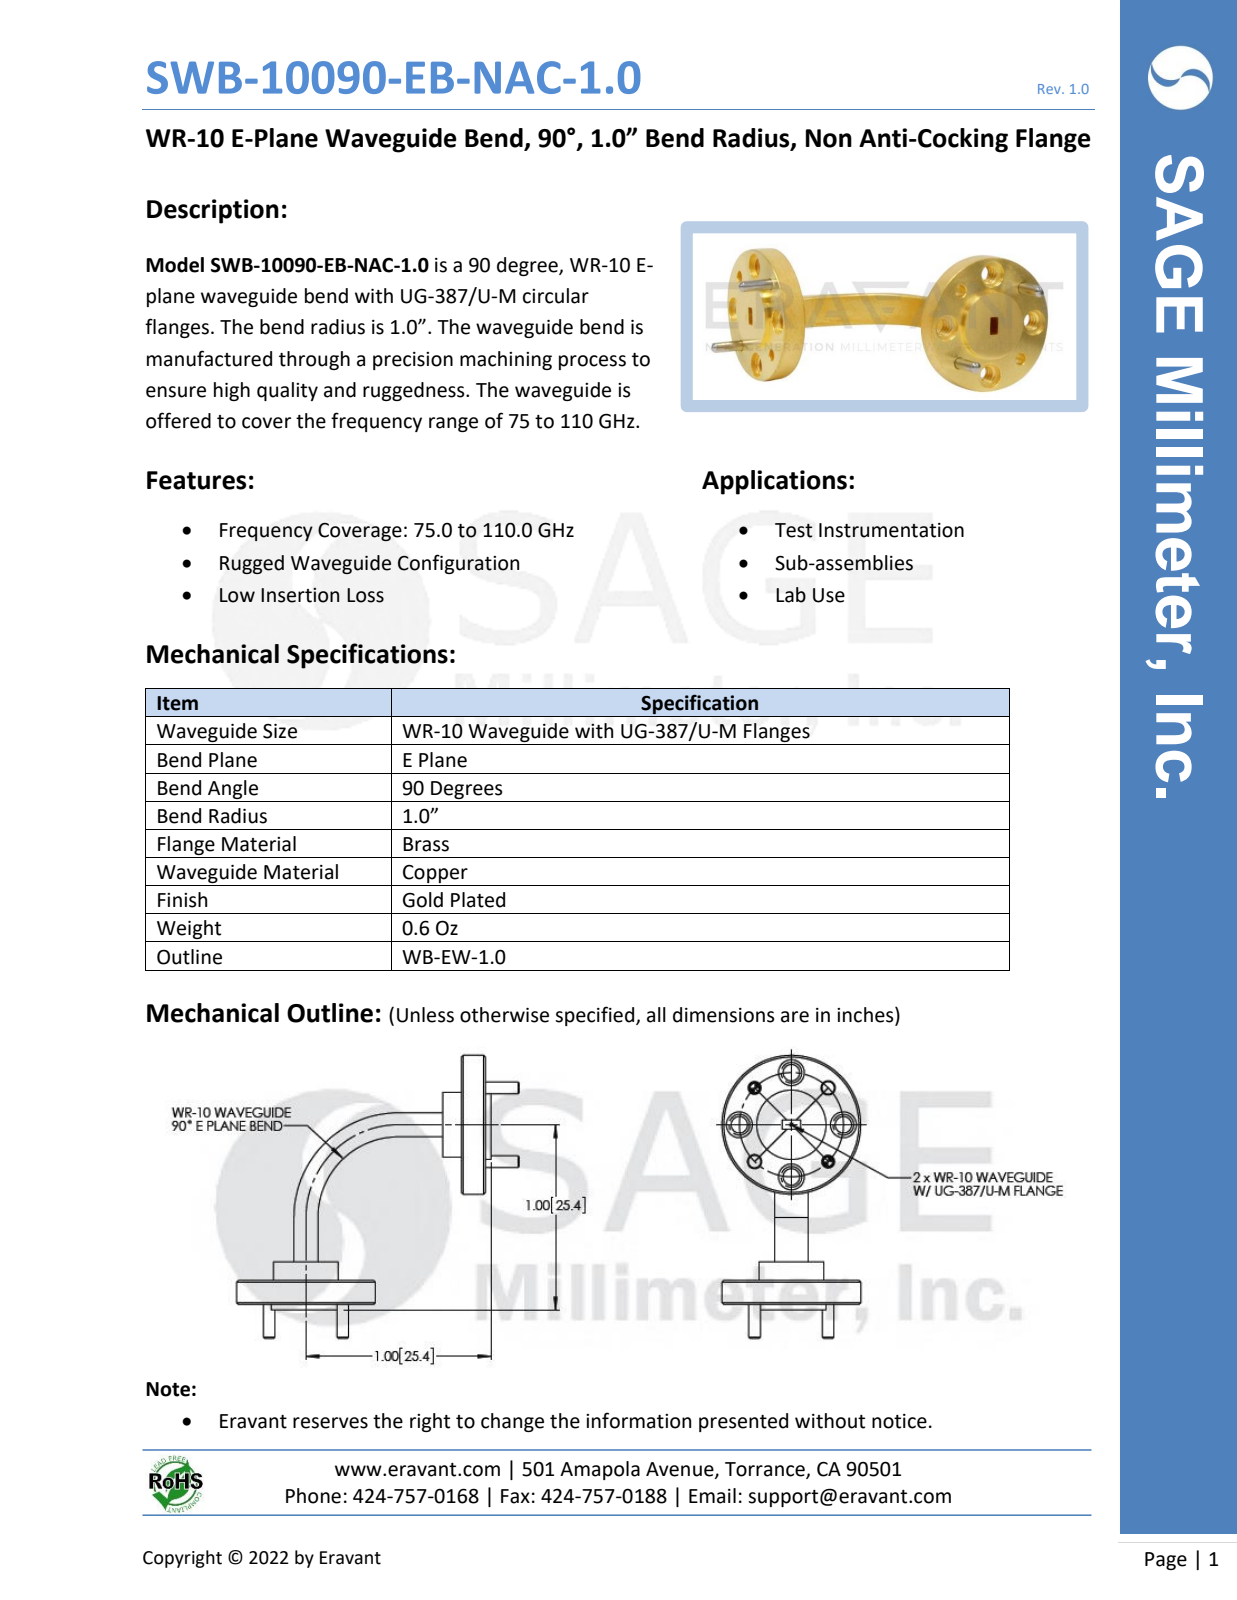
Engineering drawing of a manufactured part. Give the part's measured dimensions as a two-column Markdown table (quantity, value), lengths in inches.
| quantity | value |
| --- | --- |
| part name | WB-EW |
| STEP written by | SolidWorks 2021 (CONFIG_CONTROL_DESIGN) |
| units | inches |
| bodies | 5 solids, 150 faces (40 planar, 70 cylindrical, 40 other) |
| overall size | 1.528 × 1.527 × 0.75 |
| volume | 0.162 in³ |
| surface area | 3.991 in² |
| round holes (diameter × count) | 0.089 × 8, 0.14 × 8, 0.06 × 4, 0.067 × 4 |
| round bosses / shafts (diameter × count) | 0.063 × 4, 0.75 × 2, 0.375 × 2, 0.35 × 2 |
| partial cylindrical surfaces (radius × count) | 0.435 × 1, 0.565 × 1 |
| main face-to-face distances | 0.13, 0.03, 0.16, 0.905, 0.18, 0.1, 0.26, 0.23, 1.065, 1.035 |
| hole center spacings | 0.215, 0.398, 0.519, 0.562 |
